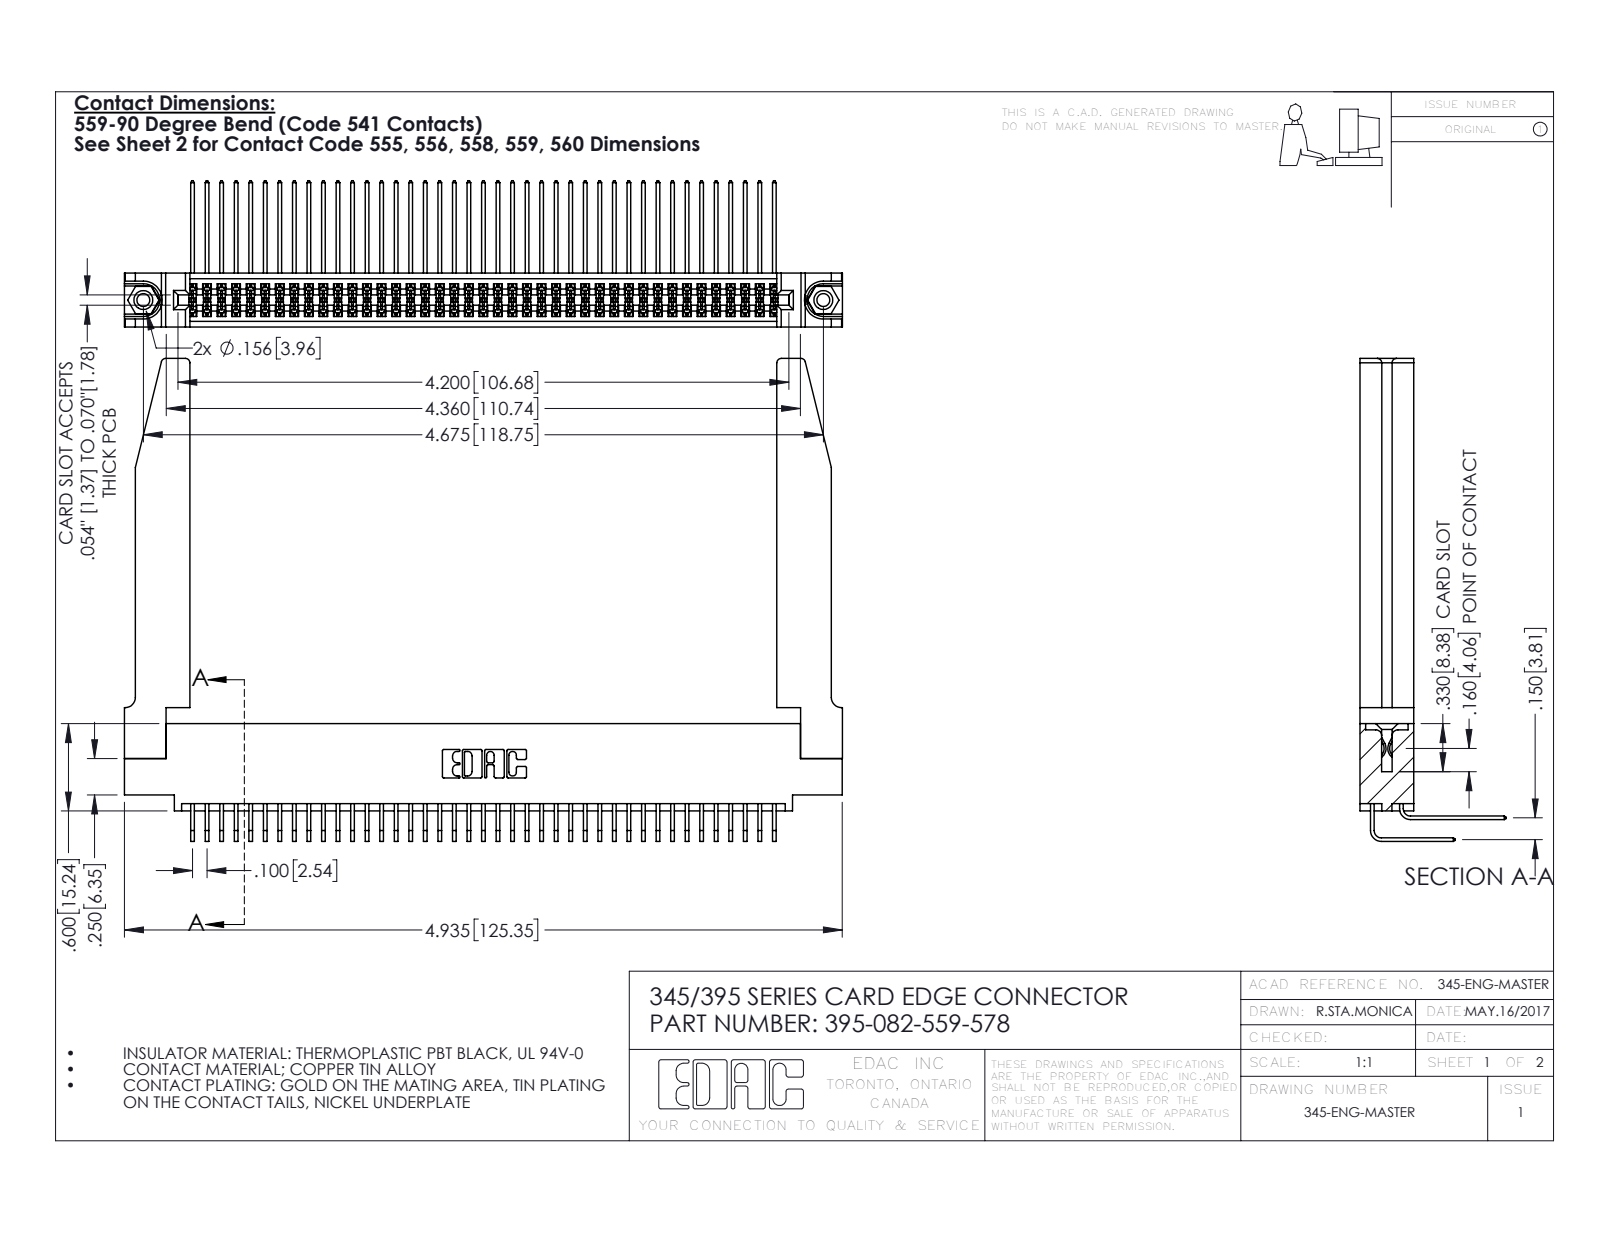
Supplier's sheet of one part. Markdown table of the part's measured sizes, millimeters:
| quantity | value |
| --- | --- |
| part name | 395-082-559-578; 345-292-001_559 Tail - 2; 345 Part_0.110 Offset - 0.156 Dia-TH; 345-292-001_558 559 Tail - 1 (+2 more) |
| STEP written by | SolidWorks 2016 (CONFIG_CONTROL_DESIGN) |
| units | millimeters |
| bodies | 87 solids, 4628 faces (3096 planar, 1480 cylindrical, 52 other) |
| overall size | 125.4 × 84.3 × 25.5 |
| volume | 20 340 mm³ |
| surface area | 27 720 mm² |
| round holes (diameter × count) | 2.3 × 2, 3.2 × 2, 4 × 2, 1.6 × 1 |
| round bosses / shafts (diameter × count) | 3.9 × 2 |
| partial cylindrical surfaces (radius × count) | 0.2 × 123, 0.3 × 22, 0.8 × 8, 0.2 × 6, 0.8 × 6, 0.7 × 3, 0.4 × 2, 0.5 × 2 |
| main face-to-face distances | 9.4, 1.8, 7.6, 5.1, 2.5, 6.9, 0.6, 5.7, 4.4, 3.8 |
| hole center spacings | 6.9, 112.8, 118.7 |
